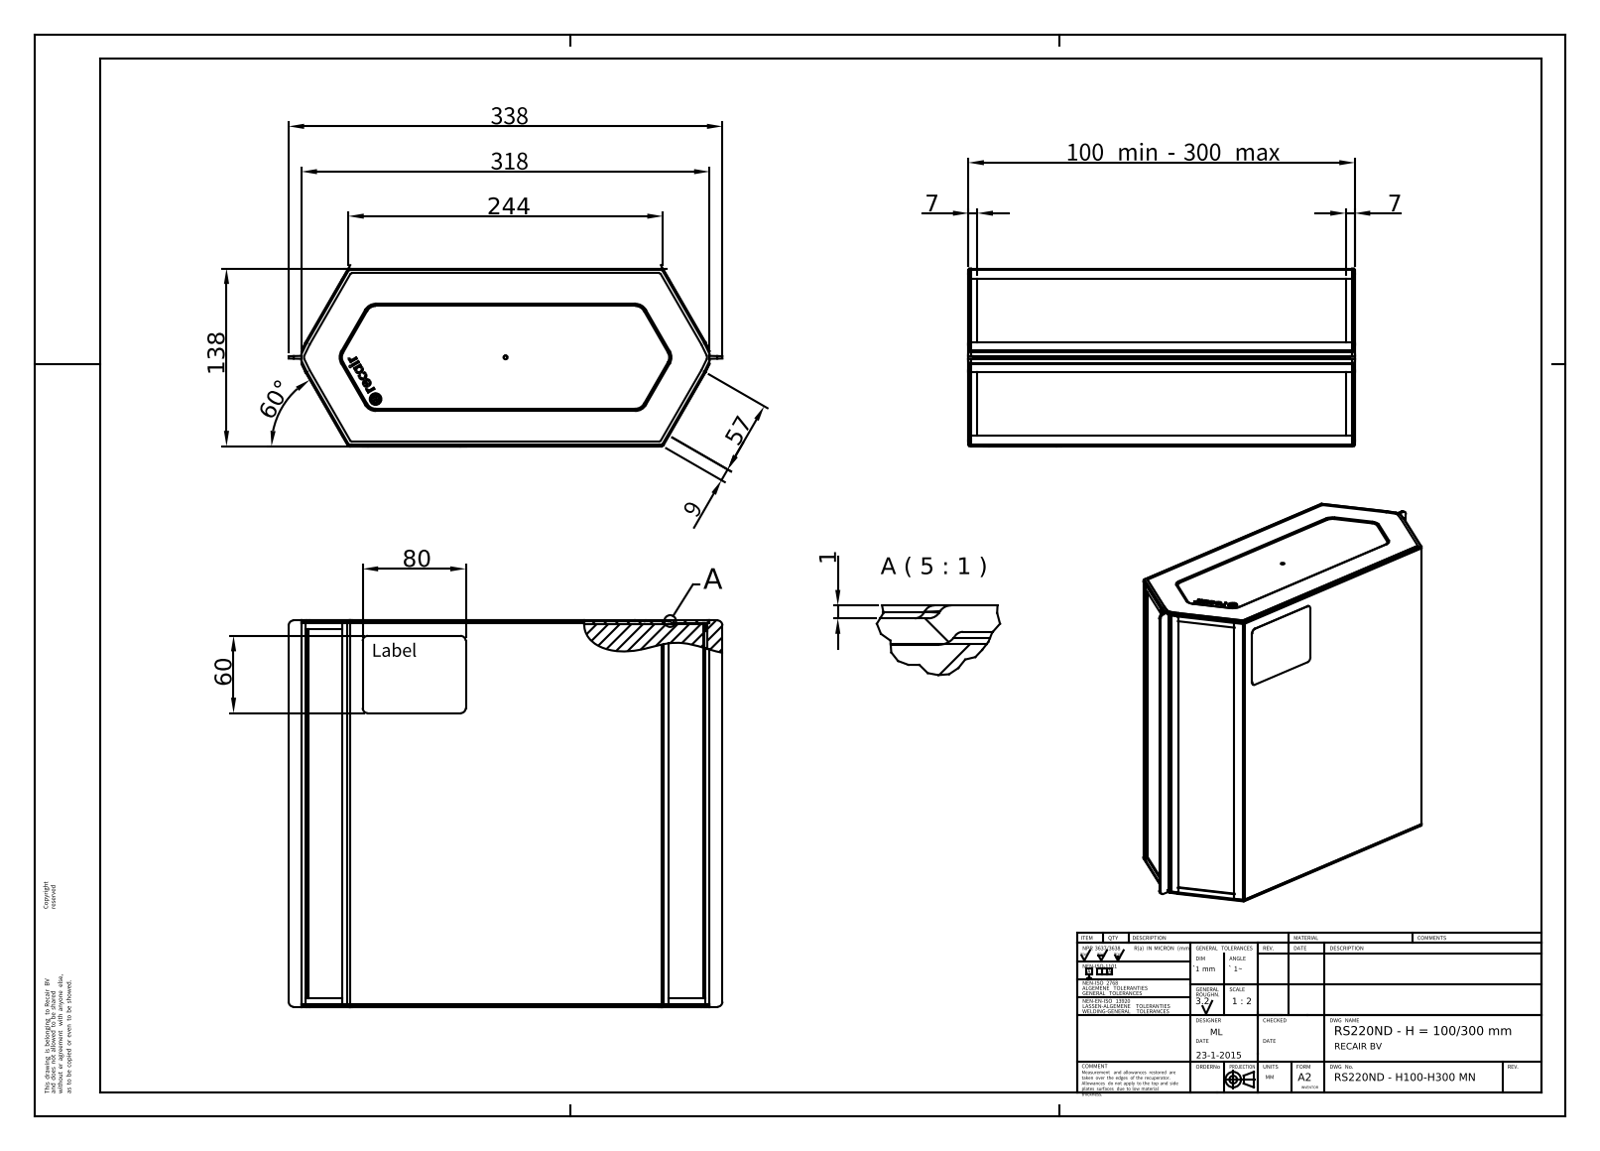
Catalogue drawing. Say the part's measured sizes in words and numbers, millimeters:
The part is named "RS220ND - H100-H300 MN". Its 3-D file was written by "Autodesk Inventor 2019 (AUTOMOTIVE_DESIGN)". It is 7 solids with 1315 faces: 439 planar, 410 cylindrical and 466 other. Overall it measures 336.76 by 300 by 138.03 millimeters. Its volume is 11 000 000 cubic millimeters and its surface area 828 895 square millimeters. Round bosses or shafts: 2 of diameter 9. Partial cylindrical surfaces (rounded edges, fillets, slot ends): 60 of radius 0.5, 54 of radius 0.15, 44 of radius 0.6, 44 of radius 1, 32 of radius 2, 16 of radius 0.7, 14 of radius 0.15, 14 of radius 4. The main face-to-face distances are 3.12, 131.42, 1.71, 136.25, 4.83, 133.13, 296.95, 134.54, 128.3, 1.
